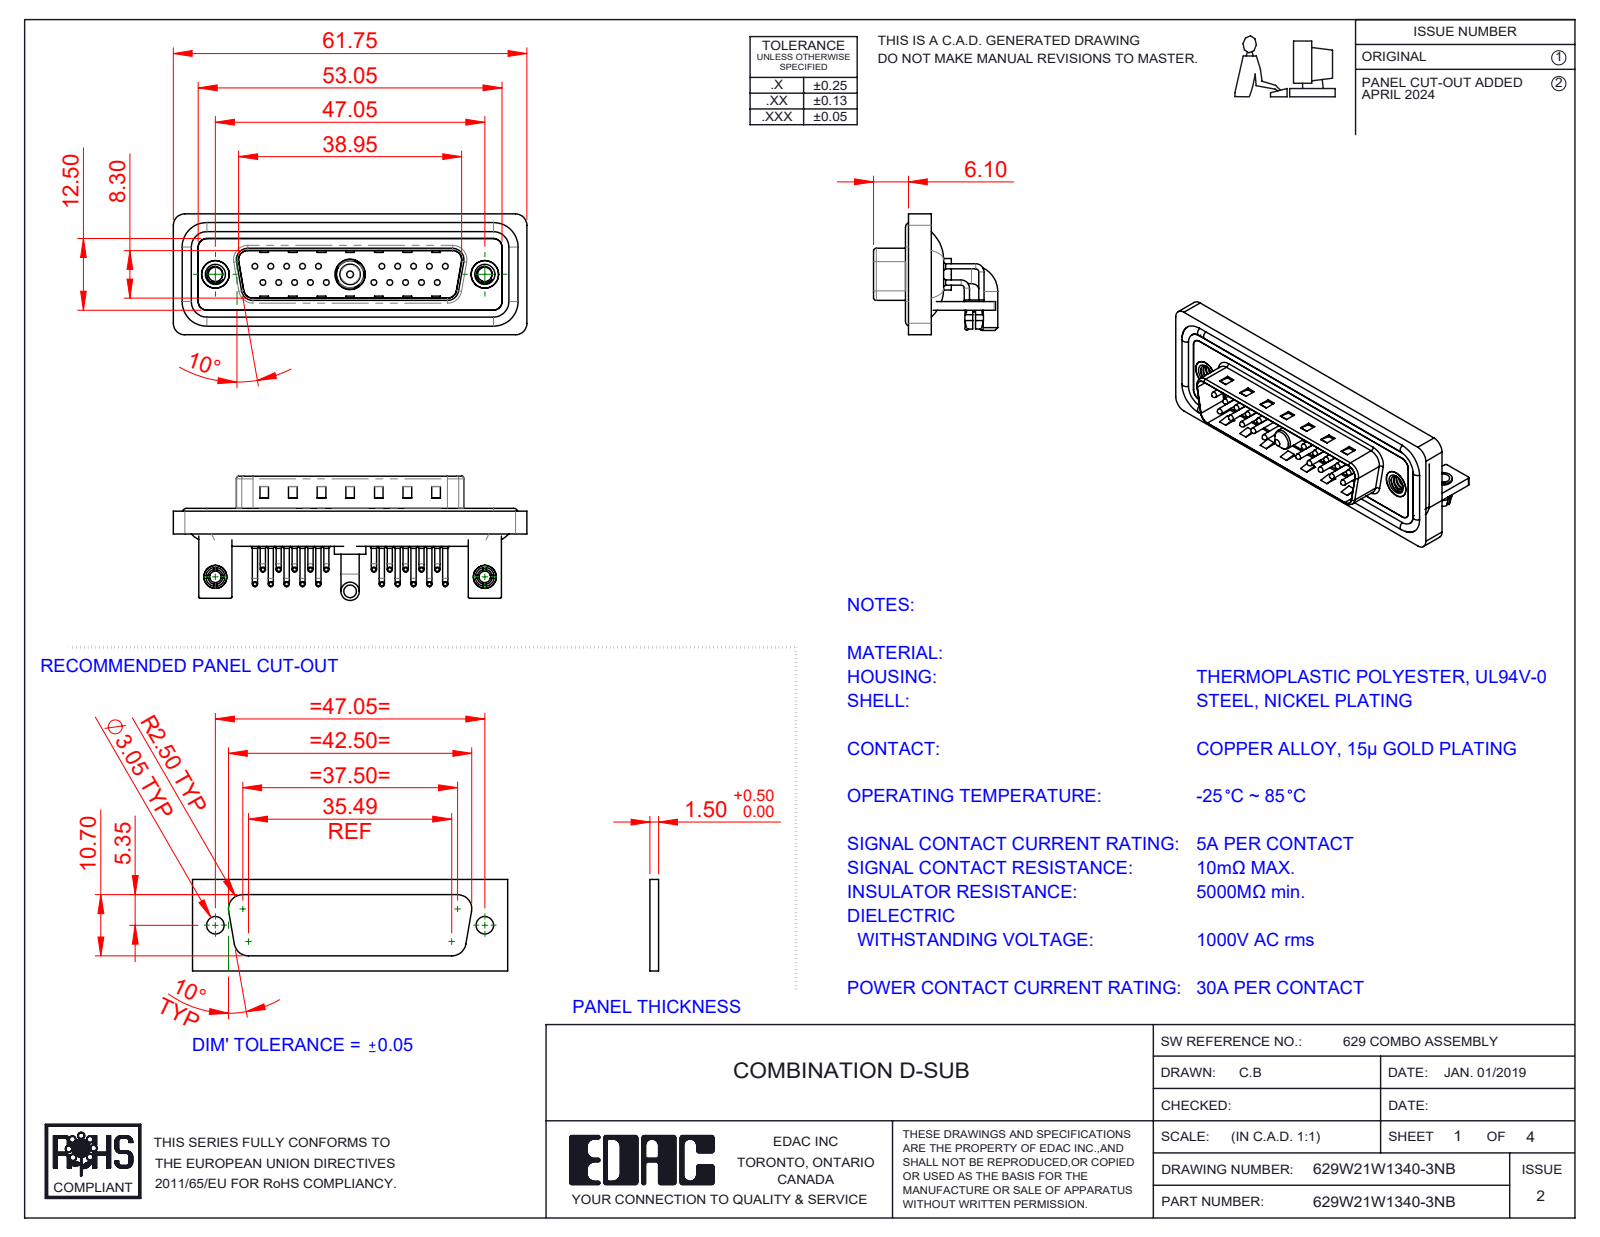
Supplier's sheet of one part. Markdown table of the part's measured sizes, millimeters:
| quantity | value |
| --- | --- |
| part name | 629Combo Threaded Rivet_B; 629Combo Board Lock; 629Combo Waterproof Housing_25 Contacts; 629Combo Shell Front_25 Contacts (+7 more) |
| STEP written by | SolidWorks 2023 (CONFIG_CONTROL_DESIGN) |
| units | millimeters |
| bodies | 33 solids, 2856 faces (1567 planar, 979 cylindrical, 310 other) |
| overall size | 61.75 × 21.7 × 21.1 |
| volume | 7 754 mm³ |
| surface area | 13 538 mm² |
| round holes (diameter × count) | 2 × 22, 0.75 × 20, 1.6 × 20, 2.5 × 4, 3.2 × 2, 4 × 2, 4.8 × 2, 5 × 2, 4.85 × 1, 5.3 × 1 |
| round bosses / shafts (diameter × count) | 0.9 × 40, 1.5 × 20, 1 × 20, 0.65 × 20, 1.6 × 4, 4.9 × 2, 4 × 2, 3.4 × 2 |
| partial cylindrical surfaces (radius × count) | 1.01 × 20, 2 × 19, 1.5 × 18, 0.25 × 16, 0.5 × 9, 1.6 × 8, 0.6 × 4, 0.65 × 4 |
| main face-to-face distances | 0.4, 0.8, 2.1, 2.9, 1.5, 1.1, 4.1, 1.6, 4.5, 3.7 |
| hole center spacings | 3.16, 2.77, 5.54, 8.31, 5.04, 19.39, 20.97, 22.16 |
